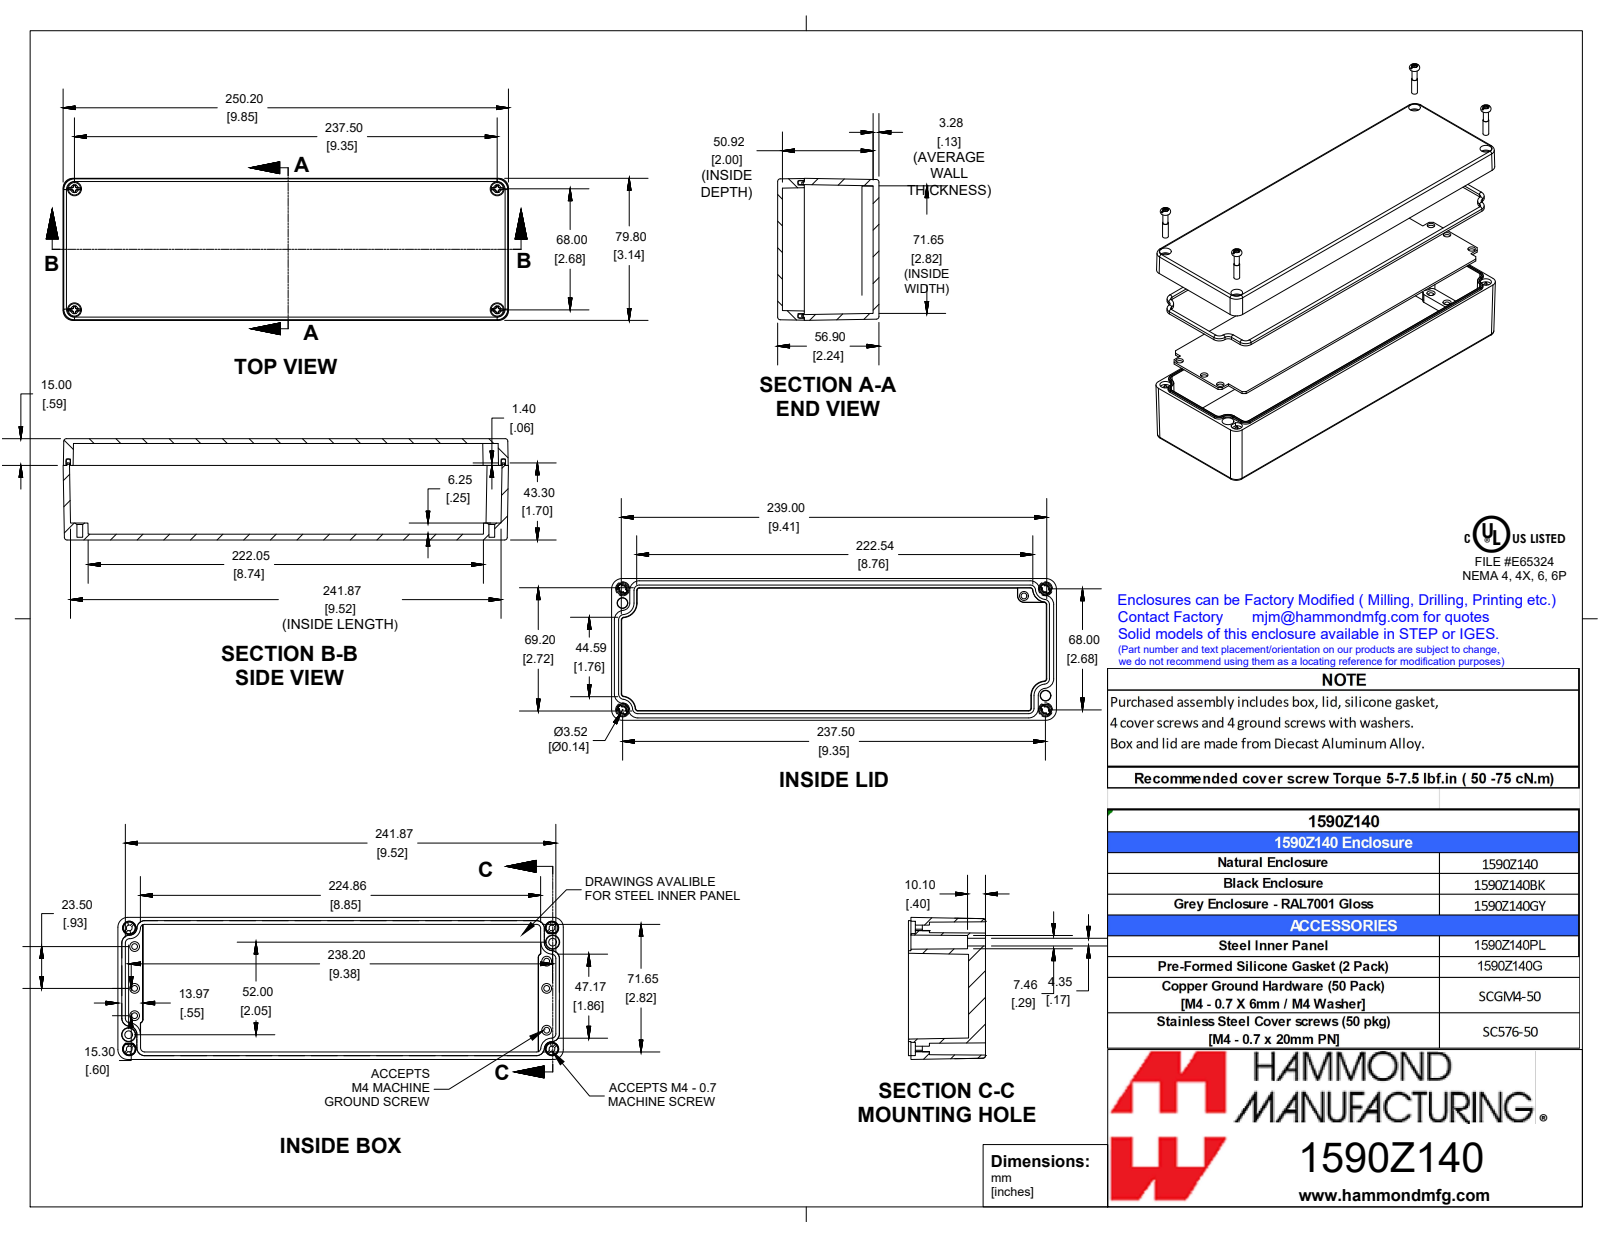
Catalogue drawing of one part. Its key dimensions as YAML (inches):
part_name: "1590Z140GY"
step_written_by: "SolidWorks 2019 (CONFIG_CONTROL_DESIGN)"
units: inches
bodies: {solids: 8, faces: 598, planar: 329, cylindrical: 125, other: 144}
overall_size: [9.85, 3.142, 2.24]
volume: 17.49
surface_area: 307.4
round_holes:
  - {diameter: 0.128, count: 11}
  - {diameter: 0.197, count: 6}
  - {diameter: 0.228, count: 4}
  - {diameter: 0.309, count: 4}
  - {diameter: 0.171, count: 2}
round_bosses_or_shafts:
  - {diameter: 0.118, count: 6}
  - {diameter: 0.276, count: 4}
  - {diameter: 0.153, count: 4}
  - {diameter: 0.135, count: 4}
partial_cylinders:
  - {radius: 0.01, count: 12}
  - {radius: 0.059, count: 8}
  - {radius: 0.118, count: 8}
  - {radius: 0.213, count: 8}
  - {radius: 0.236, count: 6}
  - {radius: 0.069, count: 4}
  - {radius: 0.091, count: 4}
  - {radius: 0.128, count: 4}
face_to_face_distances: [2.24, 0.375, 1.865, 0.246, 2.134, 1.759, 0.106, 0.129, 2.005, 2.111]
hole_center_spacings: [0.602, 0.925, 1.344, 1.528, 0.43, 0.442, 0.746, 1.032]
